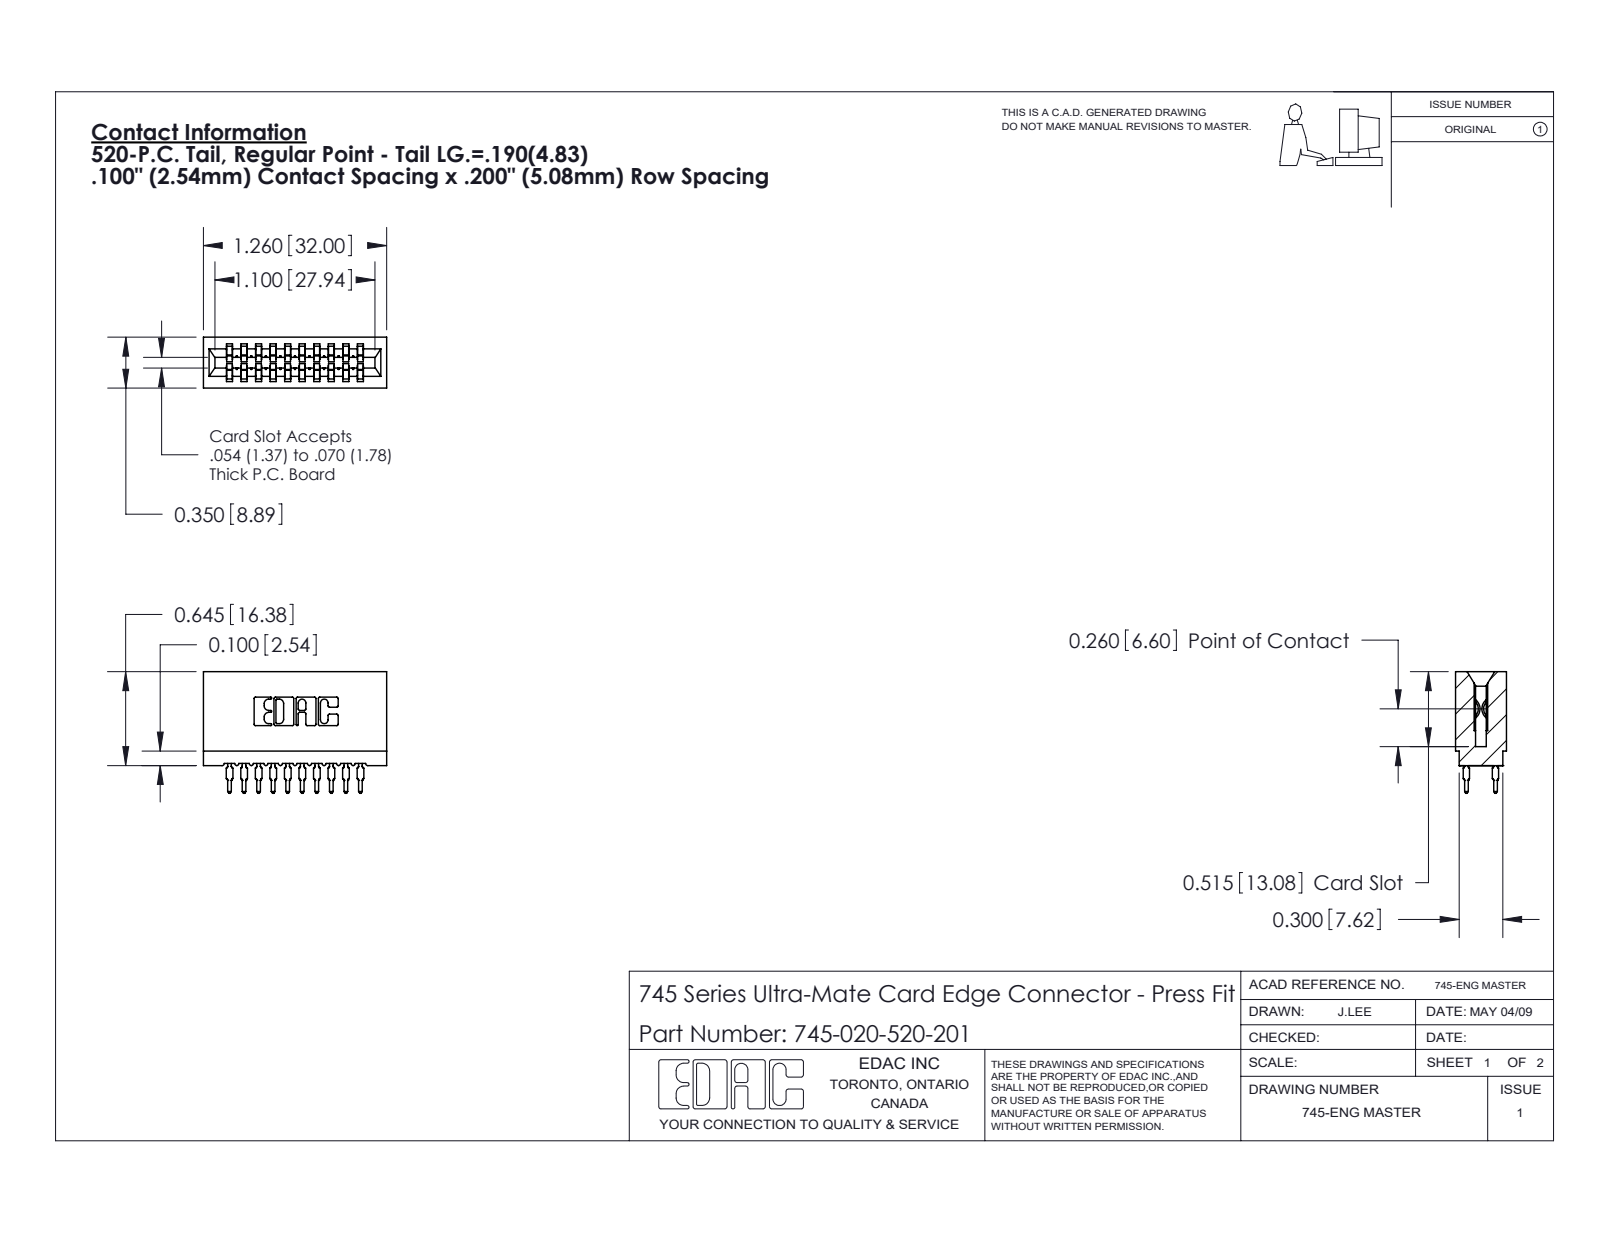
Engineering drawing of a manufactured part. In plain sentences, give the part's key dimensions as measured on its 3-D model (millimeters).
The part is named "745 Part_Insulator Option - 01; 745-292-001_520; 745-020-520-201". Its 3-D file was written by "SolidWorks 2020 (CONFIG_CONTROL_DESIGN)". It is 21 solids with 1885 faces: 975 planar, 390 cylindrical and 520 other. Overall it measures 32 by 21.2 by 8.9 millimeters. Its volume is 3 060 cubic millimeters and its surface area 5 386 square millimeters. Partial cylindrical surfaces (rounded edges, fillets, slot ends): 40 of radius 0.5, 22 of radius 0.3, 20 of radius 0.4, 8 of radius 0.1, 8 of radius 0.3, 6 of radius 0.2, 6 of radius 0.8, 3 of radius 0.7. The main face-to-face distances are 2.5, 5.1, 7.6, 10.2, 12.7, 4, 1.5, 1.1, 6.6, 3.6.
